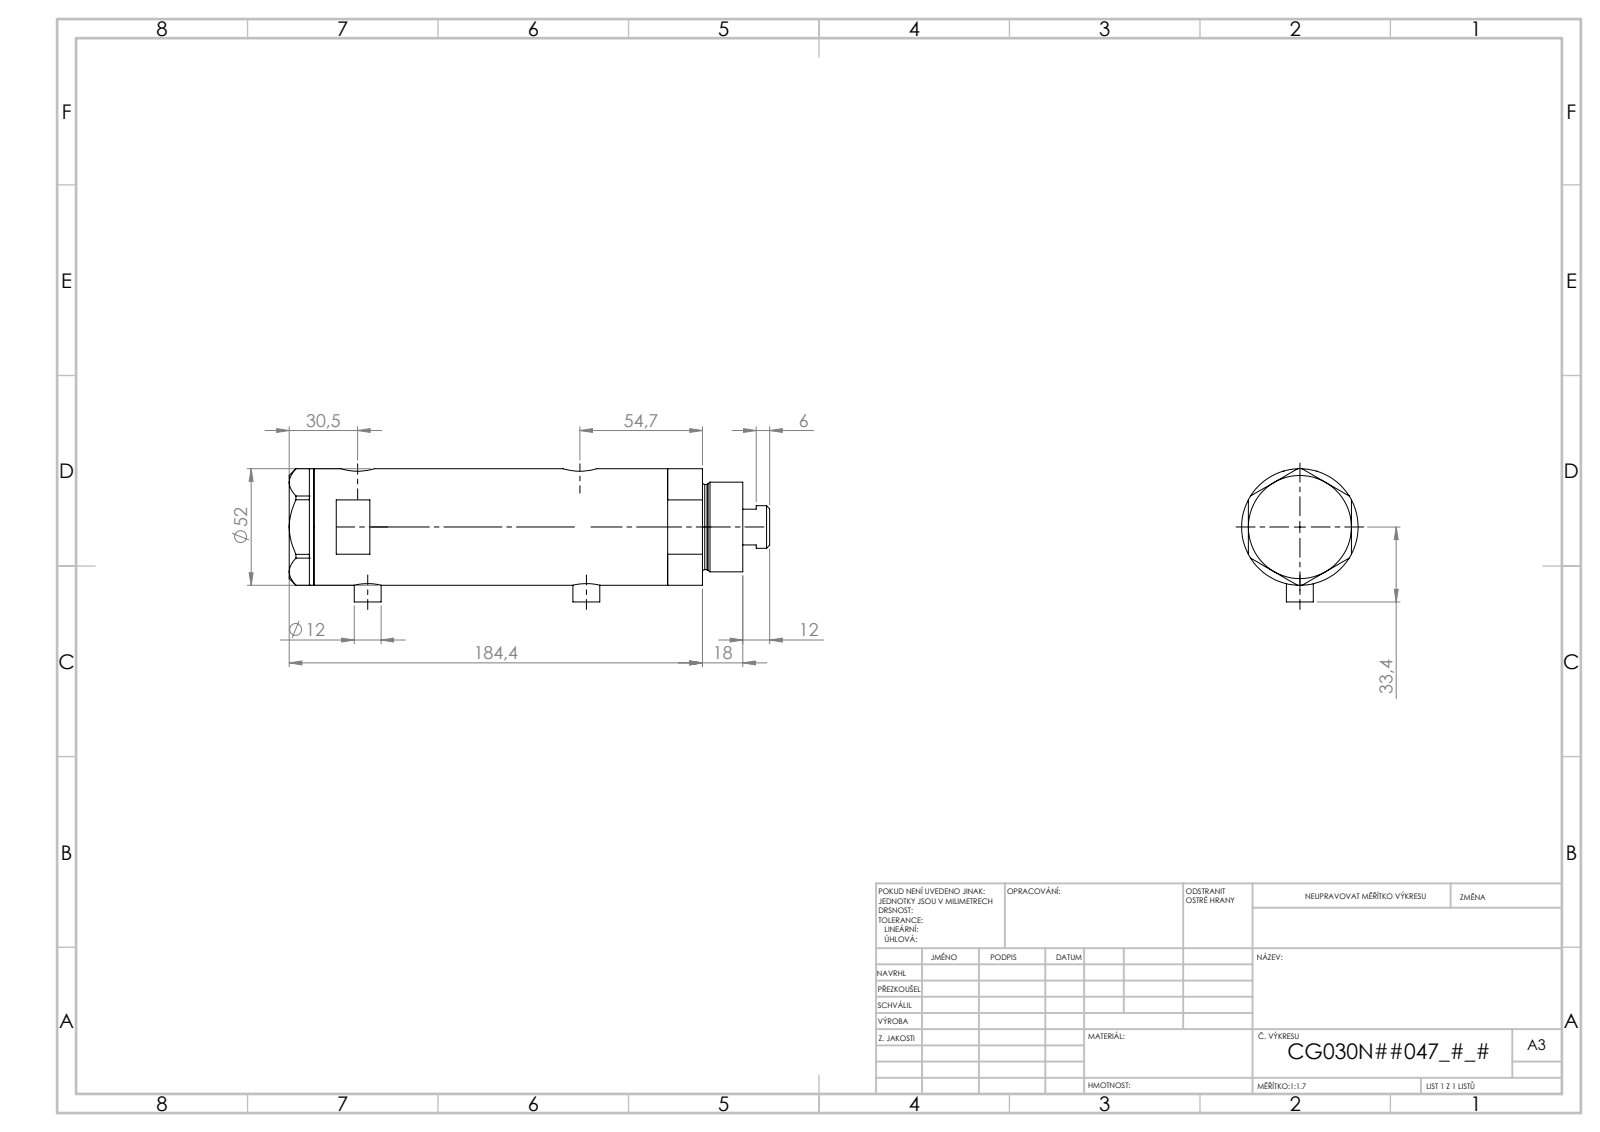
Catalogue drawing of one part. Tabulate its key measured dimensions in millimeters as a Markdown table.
| quantity | value |
| --- | --- |
| part name | V270CG_BACK; V270CG_VC; V270CG_MIDDLE; V270CG_FRONT |
| STEP written by | SolidWorks 2019 (CONFIG_CONTROL_DESIGN) |
| units | millimeters |
| bodies | 4 solids, 140 faces (67 planar, 53 cylindrical, 20 other) |
| overall size | 196.02 × 53.1 × 52 |
| volume | 348 877 mm³ |
| surface area | 80 150 mm² |
| round holes (diameter × count) | 5 × 2, 9.73 × 2, 12.5 × 2, 15 × 2, 6.5 × 1, 20 × 1, 21.5 × 1, 30 × 1, 33 × 1, 44 × 1 |
| round bosses / shafts (diameter × count) | 12 × 2, 52 × 1, 40 × 1, 38 × 1, 19 × 1 |
| main face-to-face distances | 100.54, 23.8, 76.74, 11, 34.8, 111.54, 46, 147.94, 136.94, 113.14 |
| hole center spacings | 2.9, 4.5, 73.75, 76.65, 78.25, 81.15, 2.89, 2.91 |
